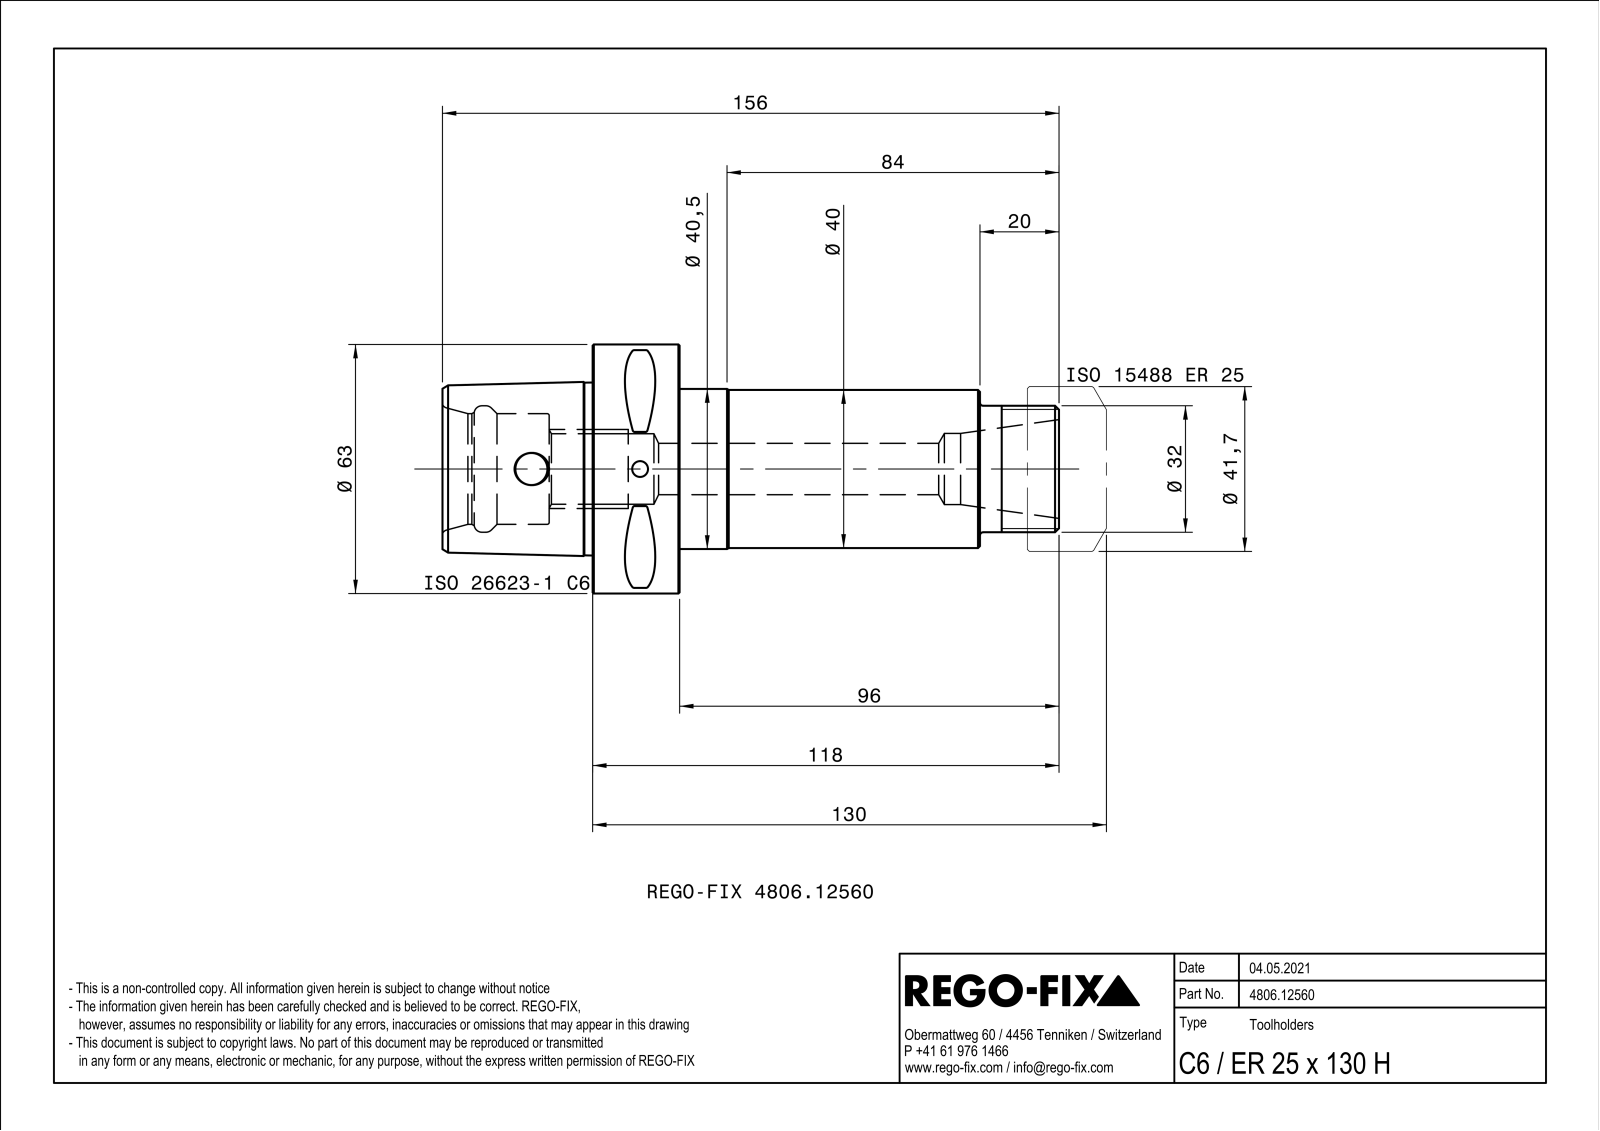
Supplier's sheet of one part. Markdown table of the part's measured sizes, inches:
| quantity | value |
| --- | --- |
| part name | NOCUT |
| STEP written by | SIEMENS PLM Software Solid Edge ST10 (AUTOMOTIVE_DESIGN) |
| units | inches |
| bodies | 1 solid, 127 faces (22 planar, 27 cylindrical, 78 other) |
| overall size | 6.142 × 2.48 × 2.48 |
| volume | 11.47 in³ |
| surface area | 55.49 in² |
| round holes (diameter × count) | 0.157 × 1, 0.319 × 1, 0.512 × 1, 0.702 × 1, 0.709 × 1, 1.102 × 1 |
| round bosses / shafts (diameter × count) | 2.48 × 1, 1.594 × 1, 1.575 × 1, 1.26 × 1 |
| partial cylindrical surfaces (radius × count) | 0.02 × 8, 0.197 × 1 |
| main face-to-face distances | 0.866, 2.362, 1.496, 2.992, 3.858, 5.354, 0.98, 4.291, 1.299, 0.433 |
| hole center spacings | 1.083 |
